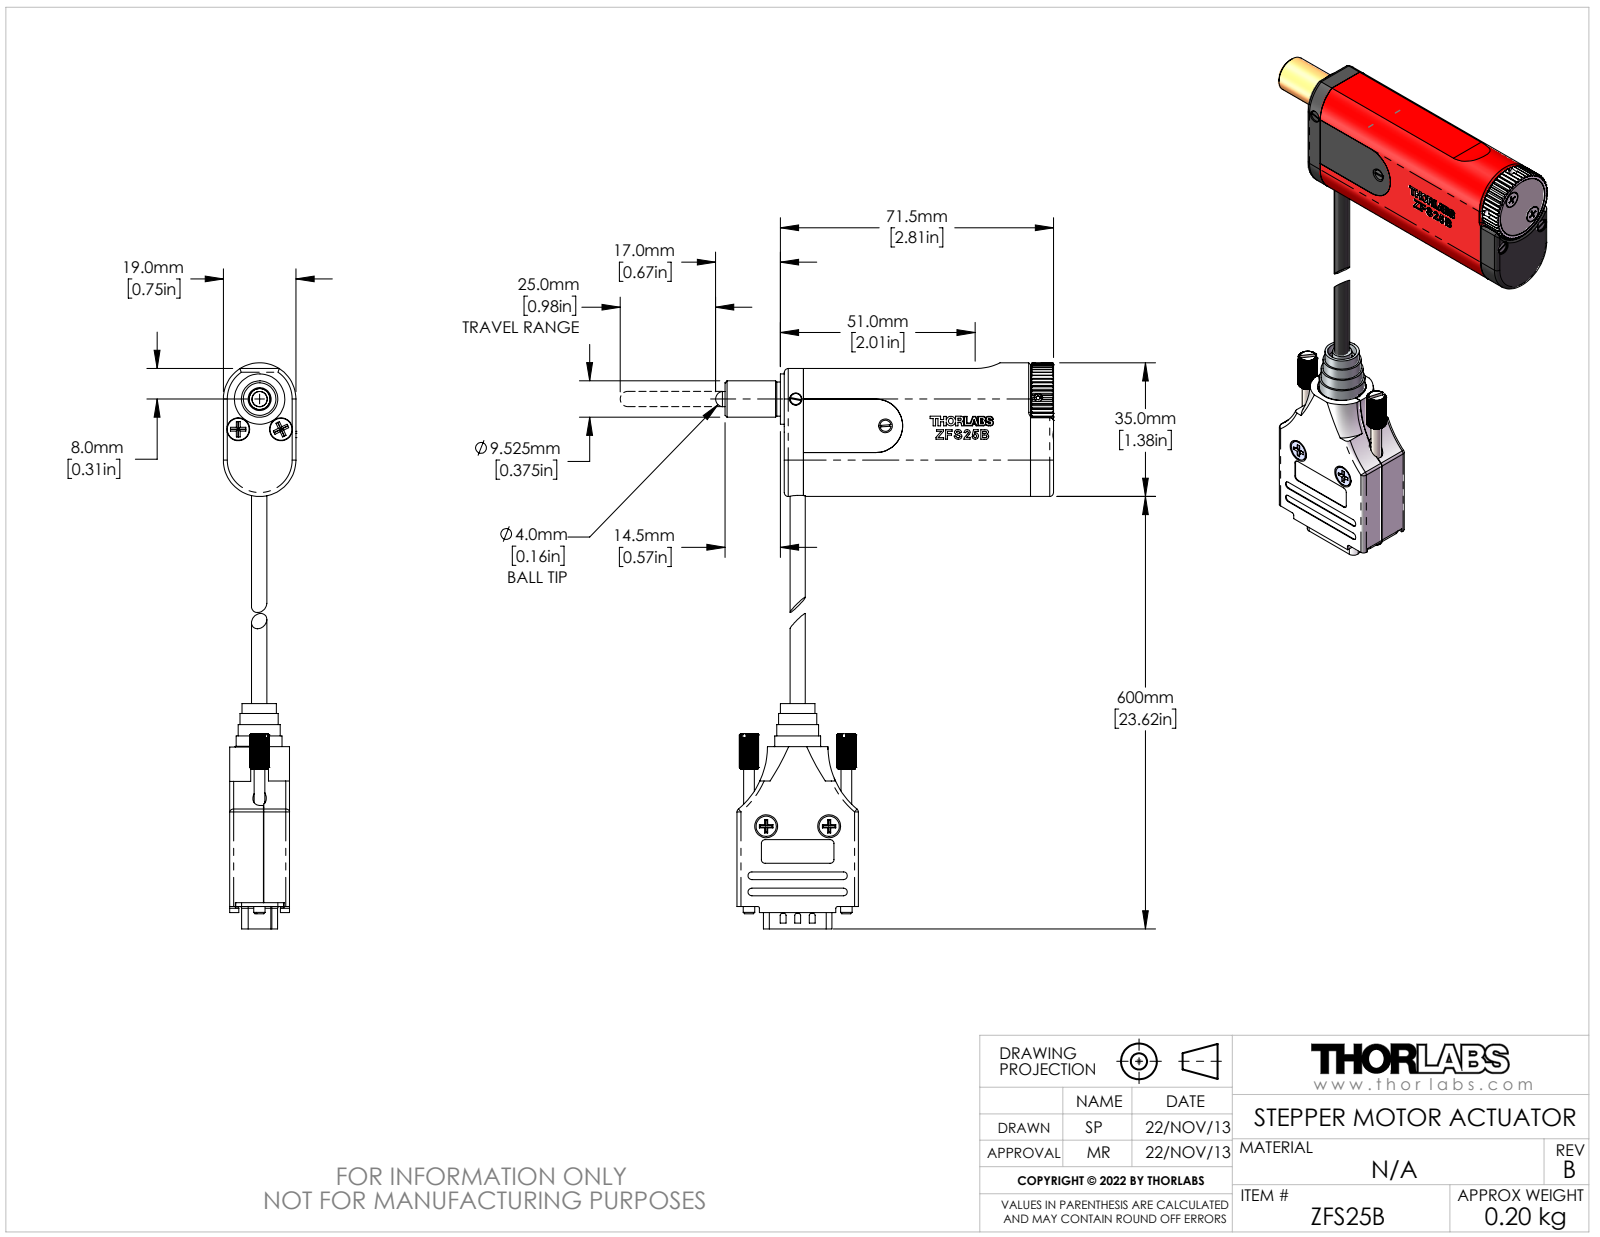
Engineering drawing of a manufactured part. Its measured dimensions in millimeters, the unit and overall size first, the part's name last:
Units: millimetres
Overall size (bounding box): 148.22 × 88.5 × 19
Round holes (diameter × count): ⌀1.02 ×15, ⌀0.6 ×10, ⌀1.6 ×9, ⌀2.5 ×7, ⌀0.5 ×6, ⌀2.1 ×6, ⌀1.25 ×5, ⌀1.8 ×4, ⌀3.1 ×4, ⌀3.05 ×3, ⌀3.2 ×3, ⌀3.4 ×3
Round bosses / shafts (diameter × count): ⌀1.52 ×15, ⌀0.99 ×15, ⌀3 ×10, ⌀1.8 ×10, ⌀2 ×7, ⌀0.6 ×6, ⌀6 ×5, ⌀1.6 ×5
Partial cylindrical surfaces — rounded edges, fillets, slot ends (radius × count): R1 ×23, R0.25 ×16, R0.51 ×14, R0.11 ×8, R0.26 ×8, R0.38 ×8, R1.52 ×8, R1.5 ×7
Main face-to-face distances: 1, 14.2, 1.45, 18, 19, 3.12, 3.13, 15.88, 1.67, 15.87
Hole centre spacings: 3.96, 2.28, 4.57, 2.29, 6.05, 6.86, 6.04, 12.5
Volume: 43 962 mm³ · Surface area: 53 325 mm²
Bodies: 108 solids, 4566 faces (2223 planar, 1319 cylindrical, 1024 other)
Part name (STEP PRODUCT): DA0032 - M2 x 6 Long Pozi Csk; Copy of Blanking Plate^BB0692 - 9 Way D Type Shell; Copy of Clamp Part B - 8 dia^BB0692 - 9 Way D Type Shell; M3 x 8 Pozi Csk^BB0692 - 9 Way D Type Shell (+8 more)
STEP written by: SolidWorks 2022 (CONFIG_CONTROL_DESIGN)
